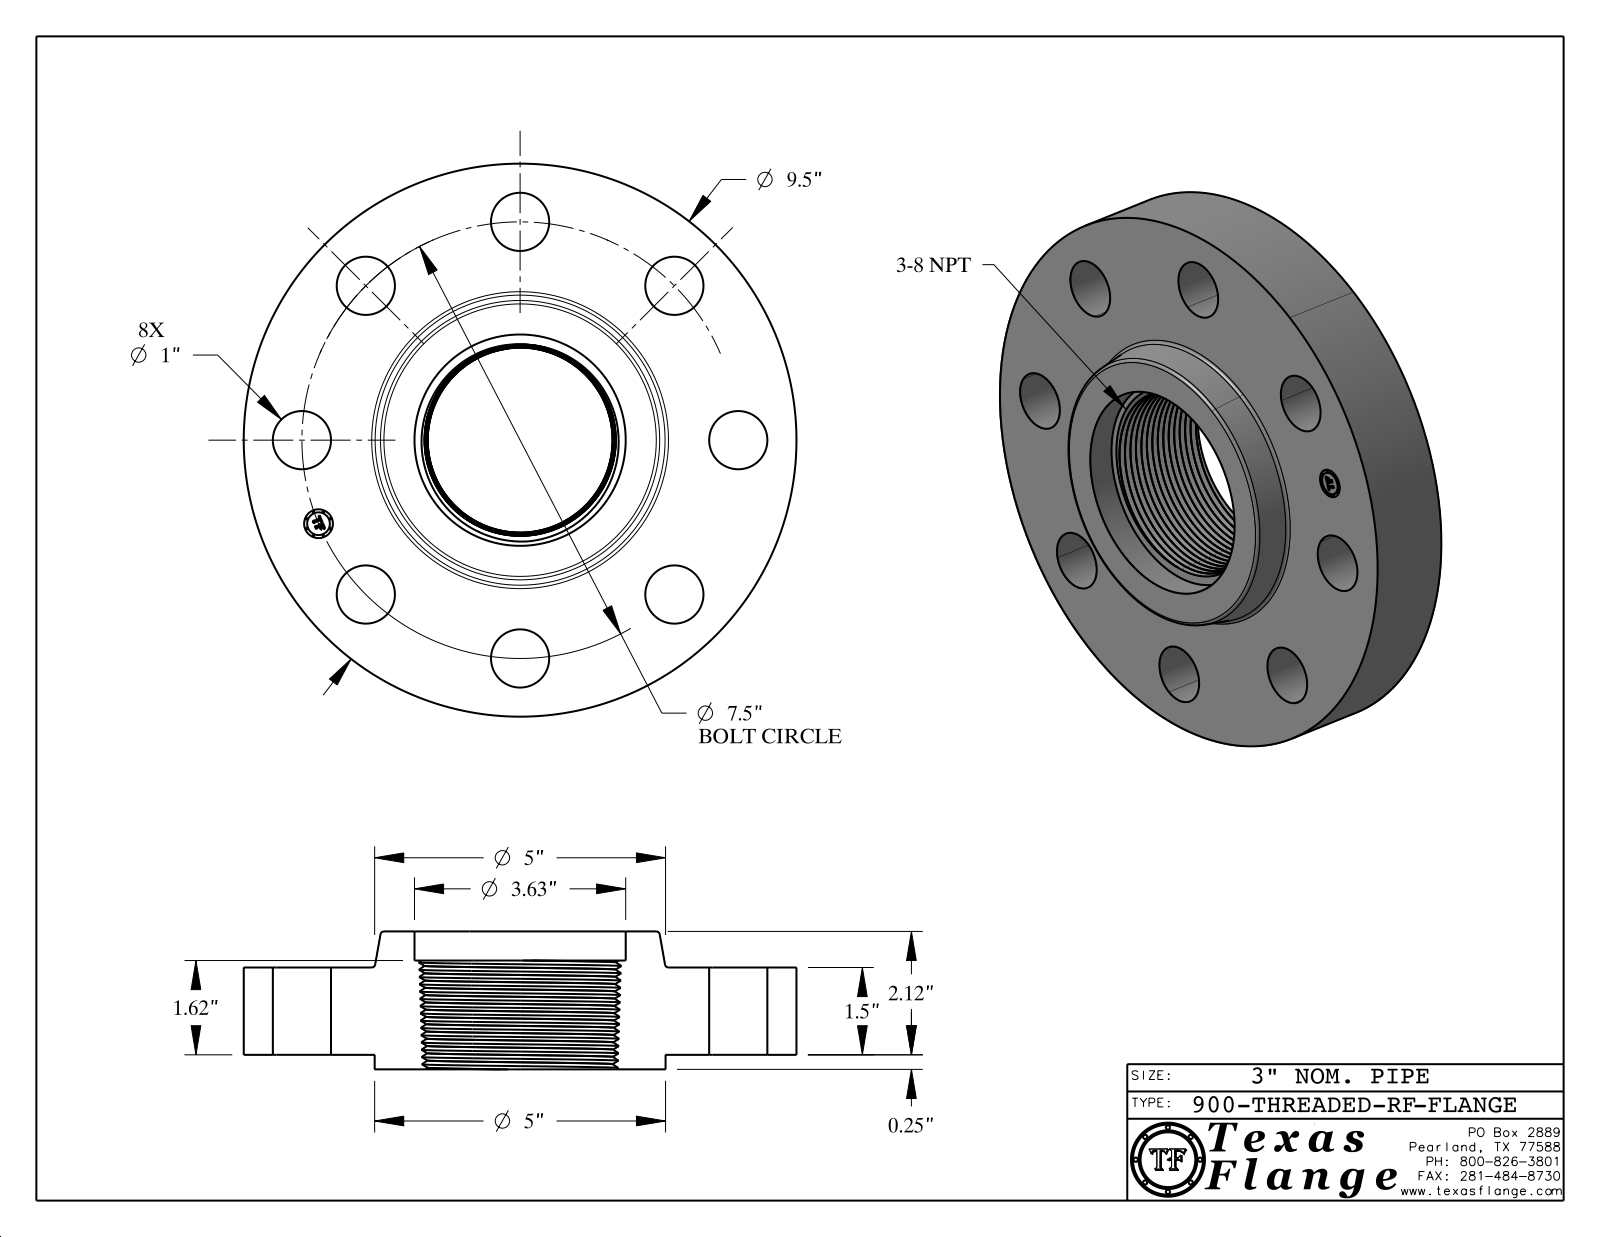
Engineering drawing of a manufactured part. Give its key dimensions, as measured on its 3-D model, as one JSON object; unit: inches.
{"part_name": "900-THREADED-RF", "step_written_by": "CATIA V5 STEP AP214 (AUTOMOTIVE_DESIGN)", "units": "inches", "bodies": {"solids": 1, "faces": 574, "planar": 370, "cylindrical": 42, "other": 162}, "overall_size": [9.5, 9.5, 2.37], "volume_in3": 91.99, "surface_area_in2": 248.1, "round_holes": [[1, 8], [0.495, 1], [3.63, 1]], "round_bosses_or_shafts": [[0.03, 8], [9.5, 1], [5, 1], [0.39, 1]], "face_to_face_distances": [1.5, 0.25, 1.75, 2.37, 2.12, 0.62, 1.87, 1.62, 0.12, 0.5], "hole_center_spacings": [3.75, 2.87, 5.303, 6.929, 1.463, 6.236, 7.356, 7.5]}
